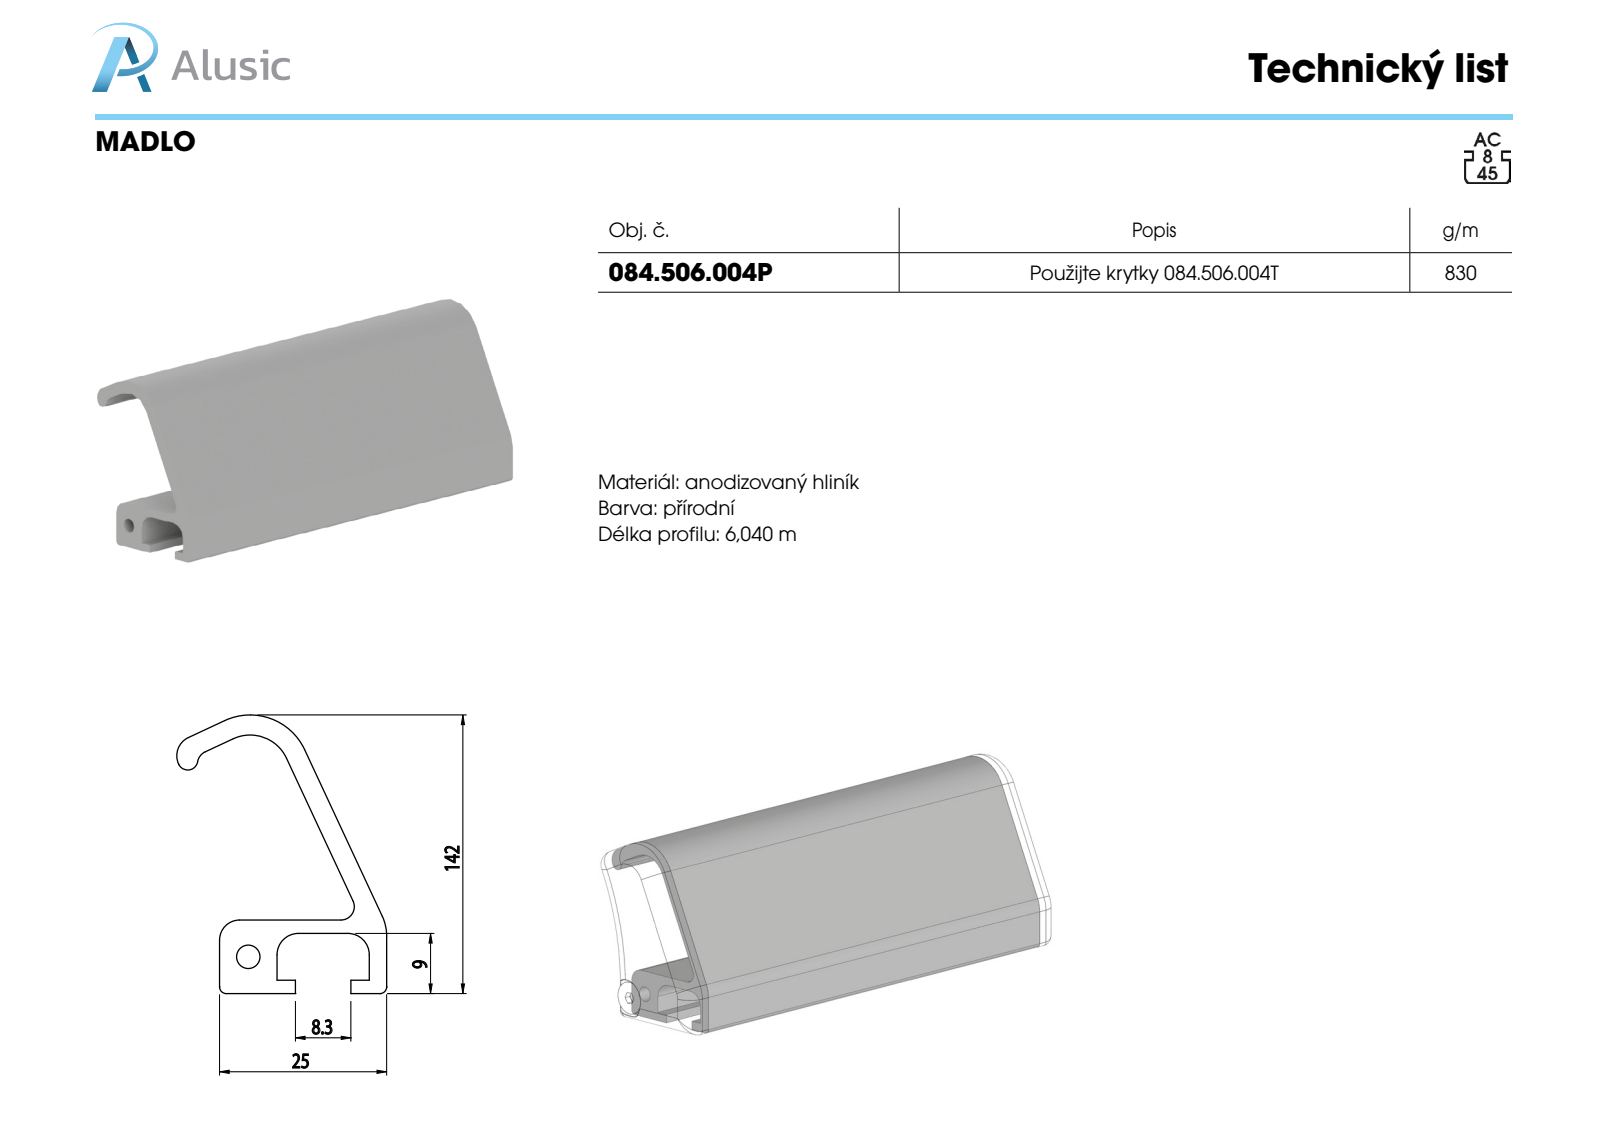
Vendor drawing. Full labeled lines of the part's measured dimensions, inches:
Part name (STEP PRODUCT): 084.506.004P
STEP written by: SolidWorks 2016 (CONFIG_CONTROL_DESIGN)
Units: inches
Bodies: 1 solid, 33 faces (18 planar, 15 cylindrical, 0 other)
Overall size (bounding box): 4.252 × 1.64 × 1.236
Volume: 1.994 in³ · Surface area: 34.52 in²
Round holes (diameter × count): ⌀0.138 ×1
Partial cylindrical surfaces — rounded edges, fillets, slot ends (radius × count): R0.039 ×2, R0.079 ×2, R0.118 ×2, R0.126 ×2, R0.059 ×1, R0.236 ×1, R0.276 ×1, R0.354 ×1
Main face-to-face distances: 0.119, 0.433, 0.079, 0.354, 0.984, 0.276, 0.118, 0.108, 0.435, 0.102
